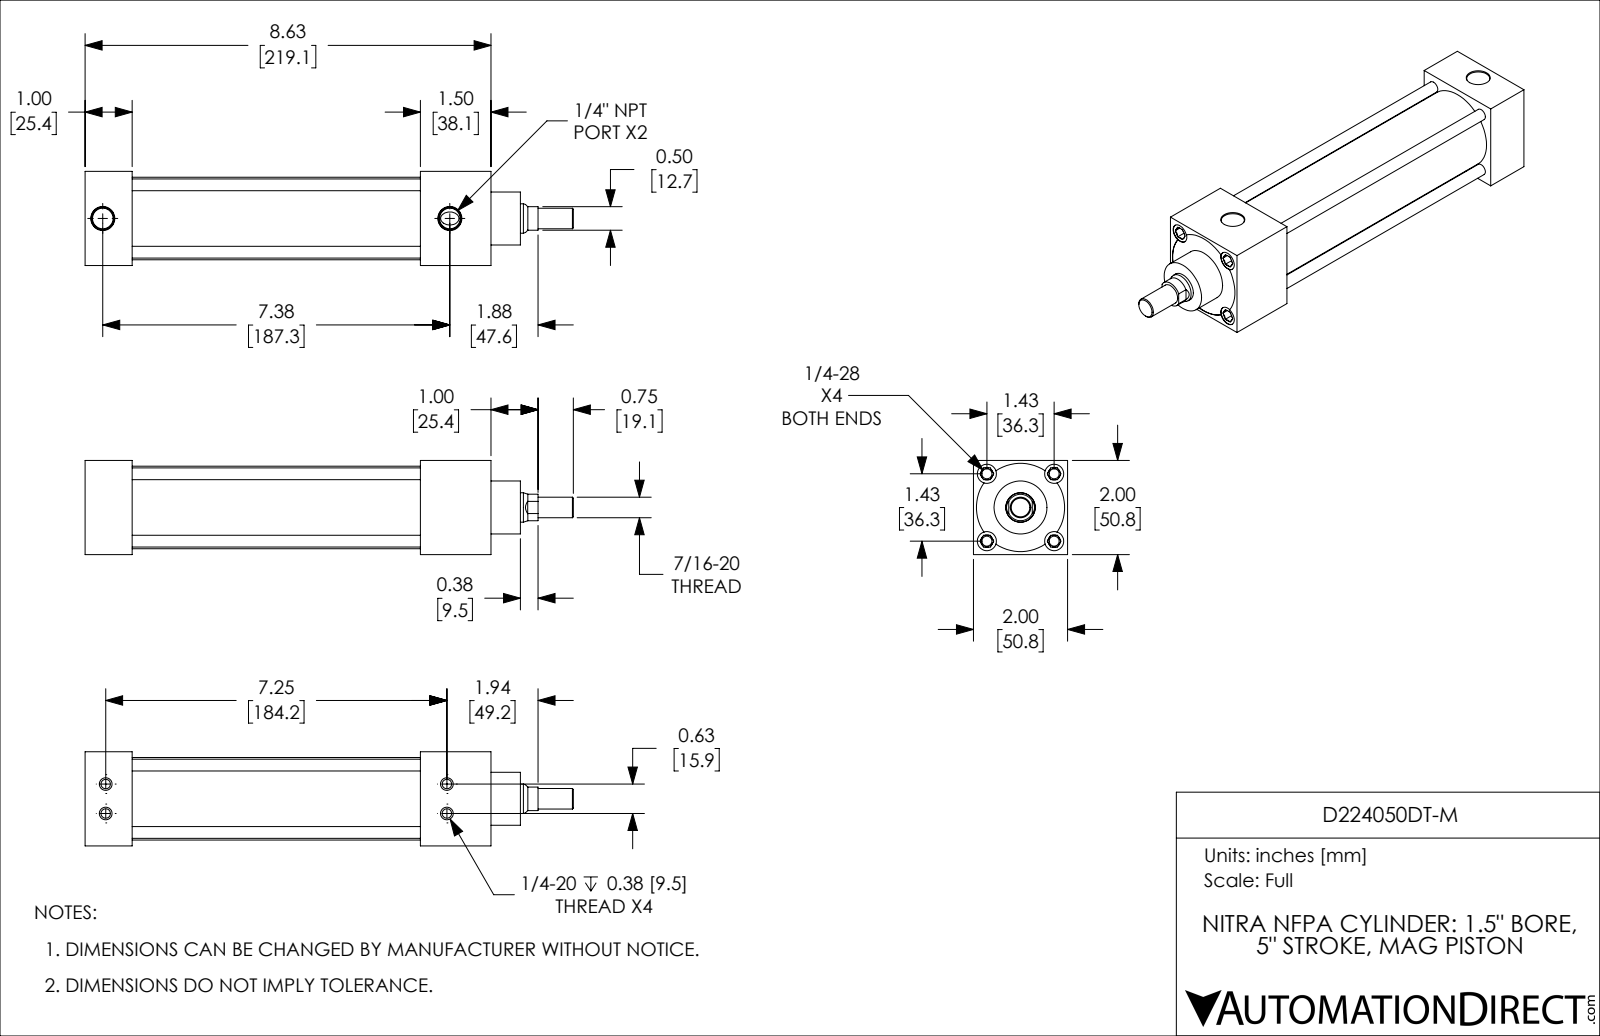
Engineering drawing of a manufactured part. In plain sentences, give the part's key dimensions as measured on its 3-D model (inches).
The part is named "D224050DT-M; D224050DT-M_BODY; D224050DT-M_PISTON_KK1". Its 3-D file was written by "SolidWorks 2019 (CONFIG_CONTROL_DESIGN)". It is 2 solids with 203 faces: 58 planar, 65 cylindrical and 80 other. Overall it measures 10.375 by 2 by 2 inches. Its volume is 18.88 cubic inches and its surface area 153.9 square inches. Round holes: 4 of diameter 0.201, 4 of diameter 0.213, 4 of diameter 0.406, 2 of diameter 0.438, 1 of diameter 0.626, 1 of diameter 1.501. Round bosses or shafts: 4 of diameter 0.25, 1 of diameter 1.751, 1 of diameter 1.499, 1 of diameter 1.125, 1 of diameter 0.624, 1 of diameter 0.437. Partial cylindrical surfaces (rounded edges, fillets, slot ends): 1 of radius 0.281, 1 of radius 0.937. The main face-to-face distances are 2, 1, 7.125, 6.125, 8.62, 7.62, 1.495, 1.125, 2.125, 5. The hole center spacings are 0.319, 1.011, 1.43, 0.625, 2.022, 7.25, 7.277, 7.319.
